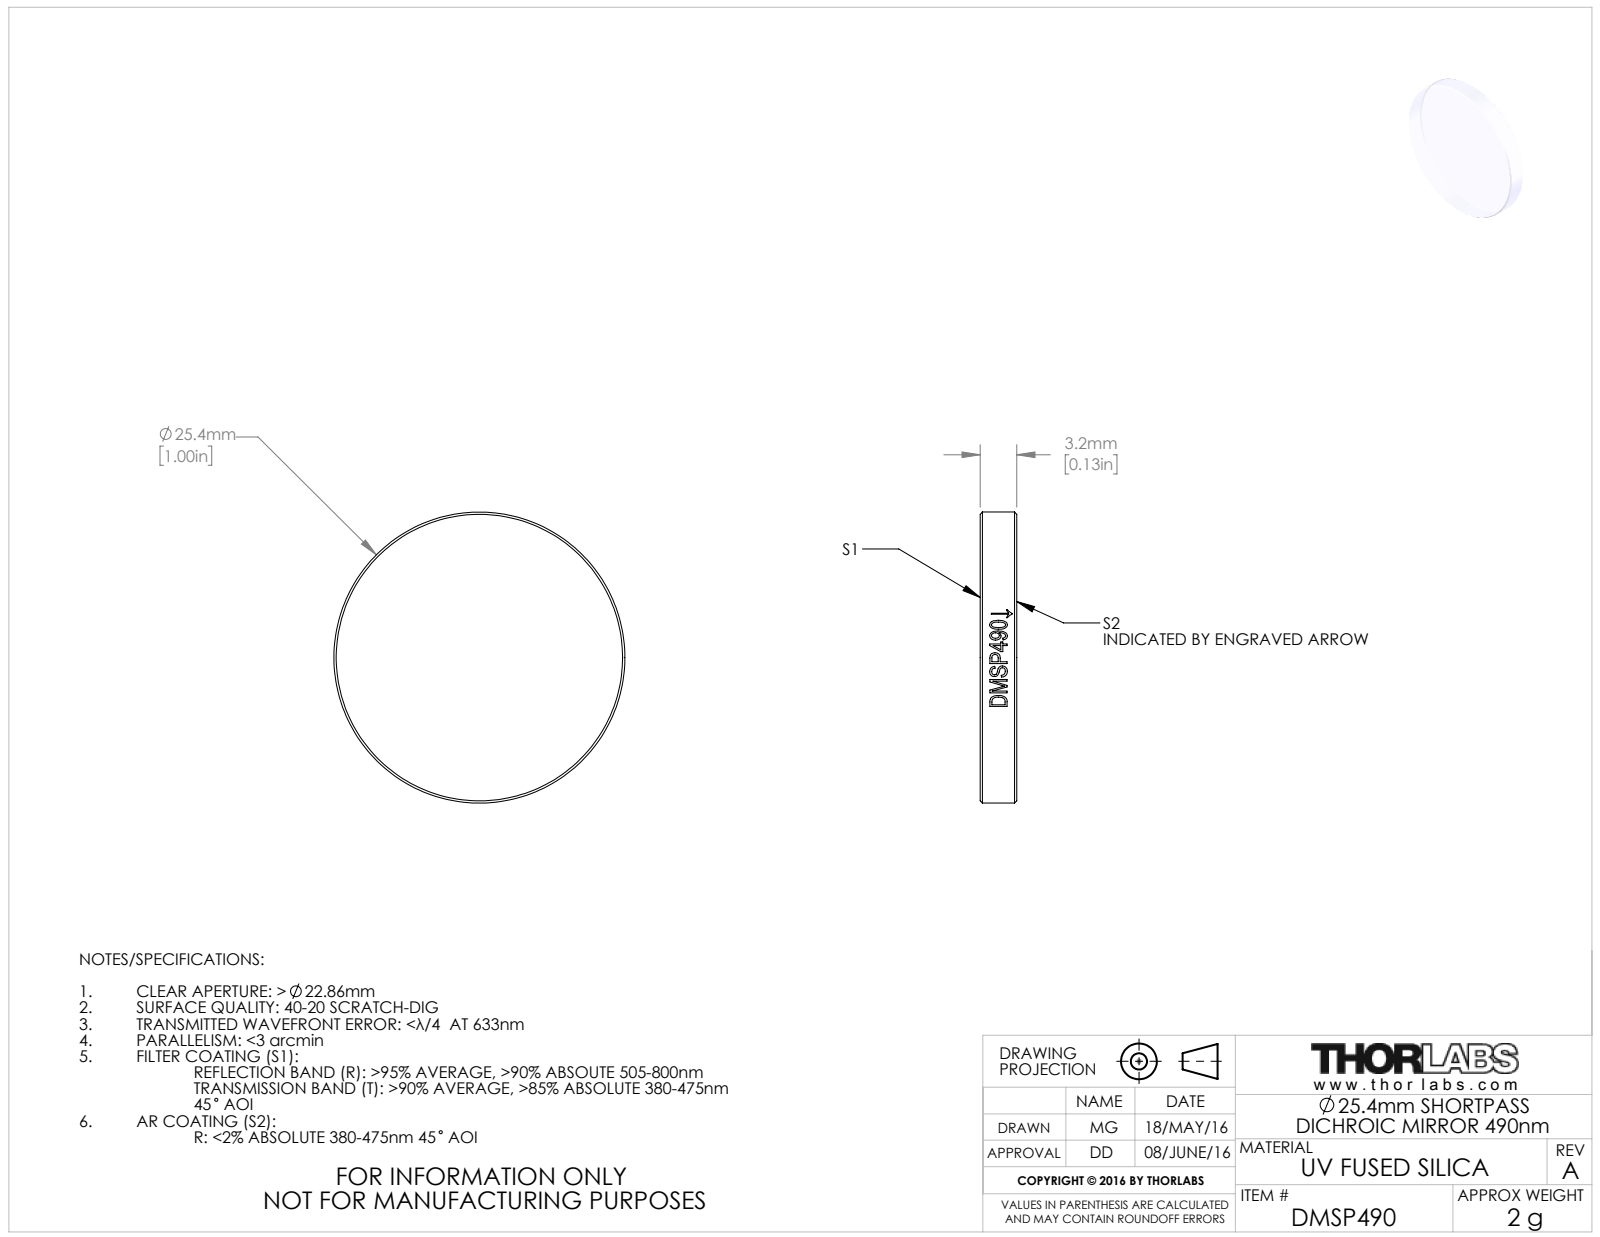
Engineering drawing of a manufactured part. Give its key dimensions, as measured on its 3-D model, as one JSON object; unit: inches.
{"part_name": "TTN045147-E0W", "step_written_by": "SolidWorks 2016 (CONFIG_CONTROL_DESIGN)", "units": "inches", "bodies": {"solids": 1, "faces": 21, "planar": 2, "cylindrical": 15, "other": 4}, "overall_size": [1, 1, 0.126], "volume_in3": 0.099, "surface_area_in2": 1.938, "round_bosses_or_shafts": [[1, 1]], "face_to_face_distances": [0.126]}
